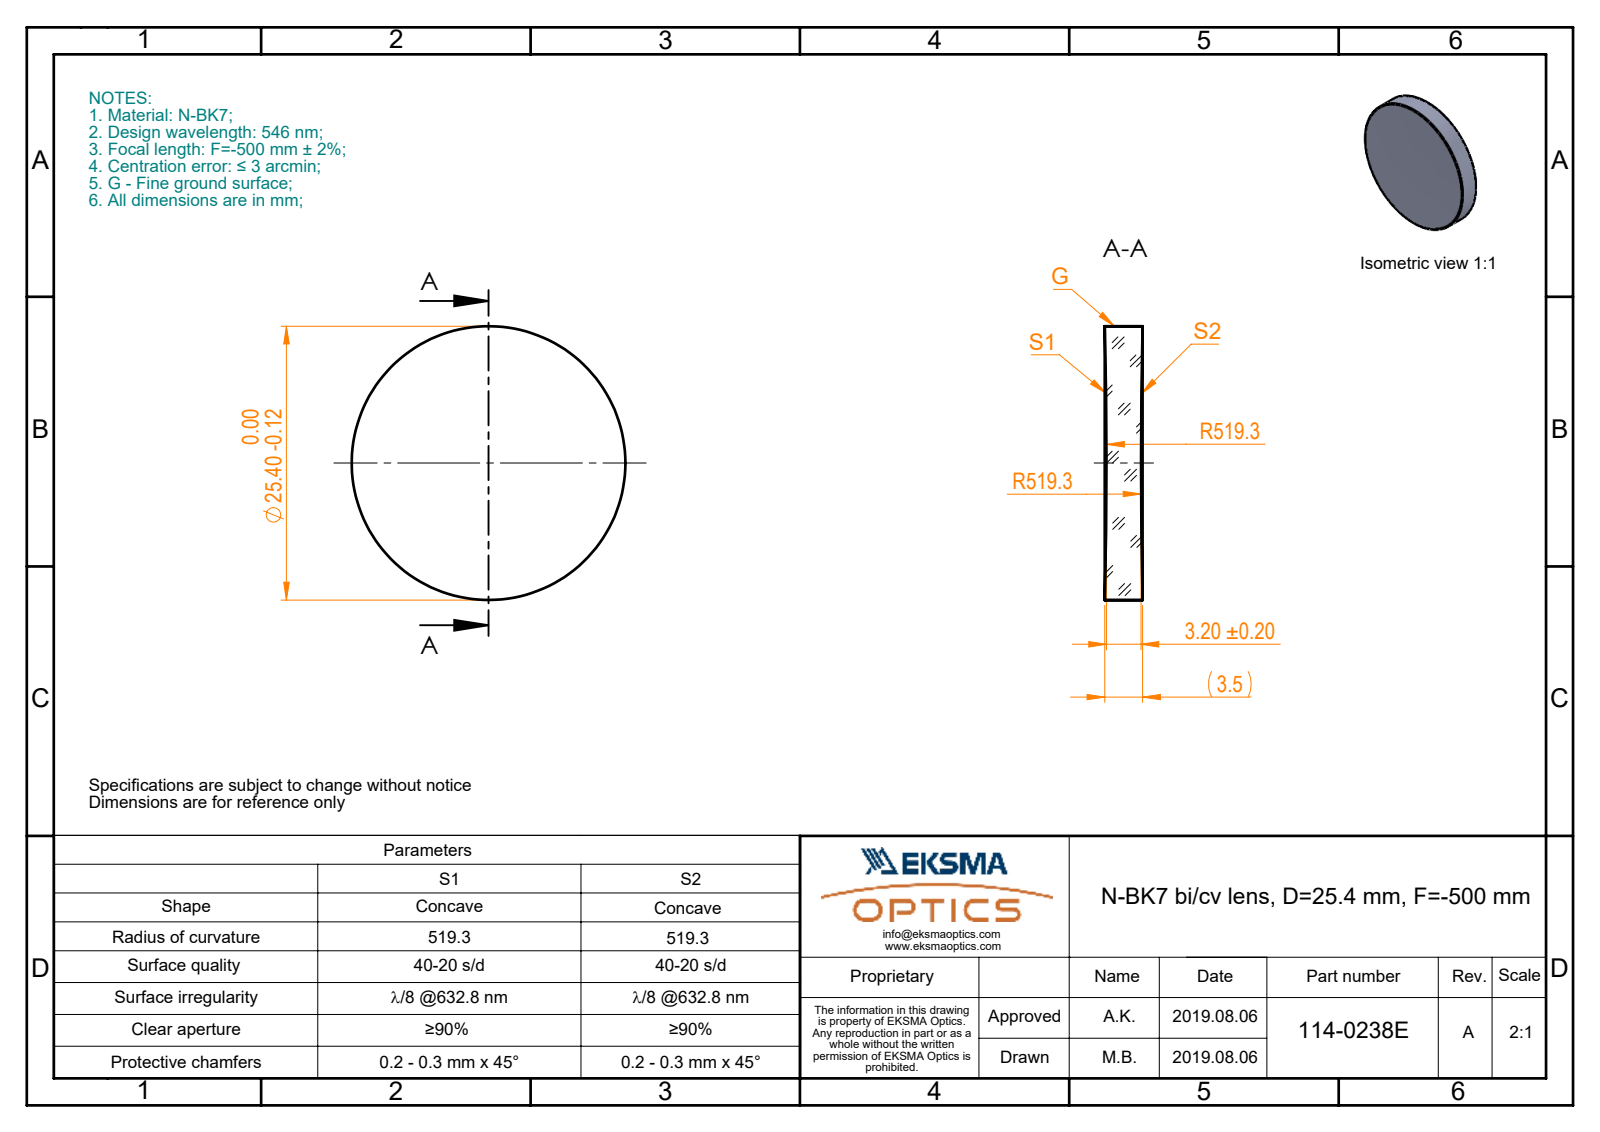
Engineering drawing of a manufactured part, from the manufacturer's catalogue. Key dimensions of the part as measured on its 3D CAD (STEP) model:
Part name (STEP PRODUCT): 114-0238E BK7 bi-cv 25.4 F-500
STEP written by: SolidWorks 2017 (CONFIG_CONTROL_DESIGN)
Units: millimetres
Bodies: 1 solid, 6 faces (0 planar, 2 cylindrical, 4 other)
Overall size (bounding box): 25.4 × 25.4 × 3.51
Volume: 1 700 mm³ · Surface area: 1 294 mm²
Round bosses / shafts (diameter × count): ⌀25.4 ×1
